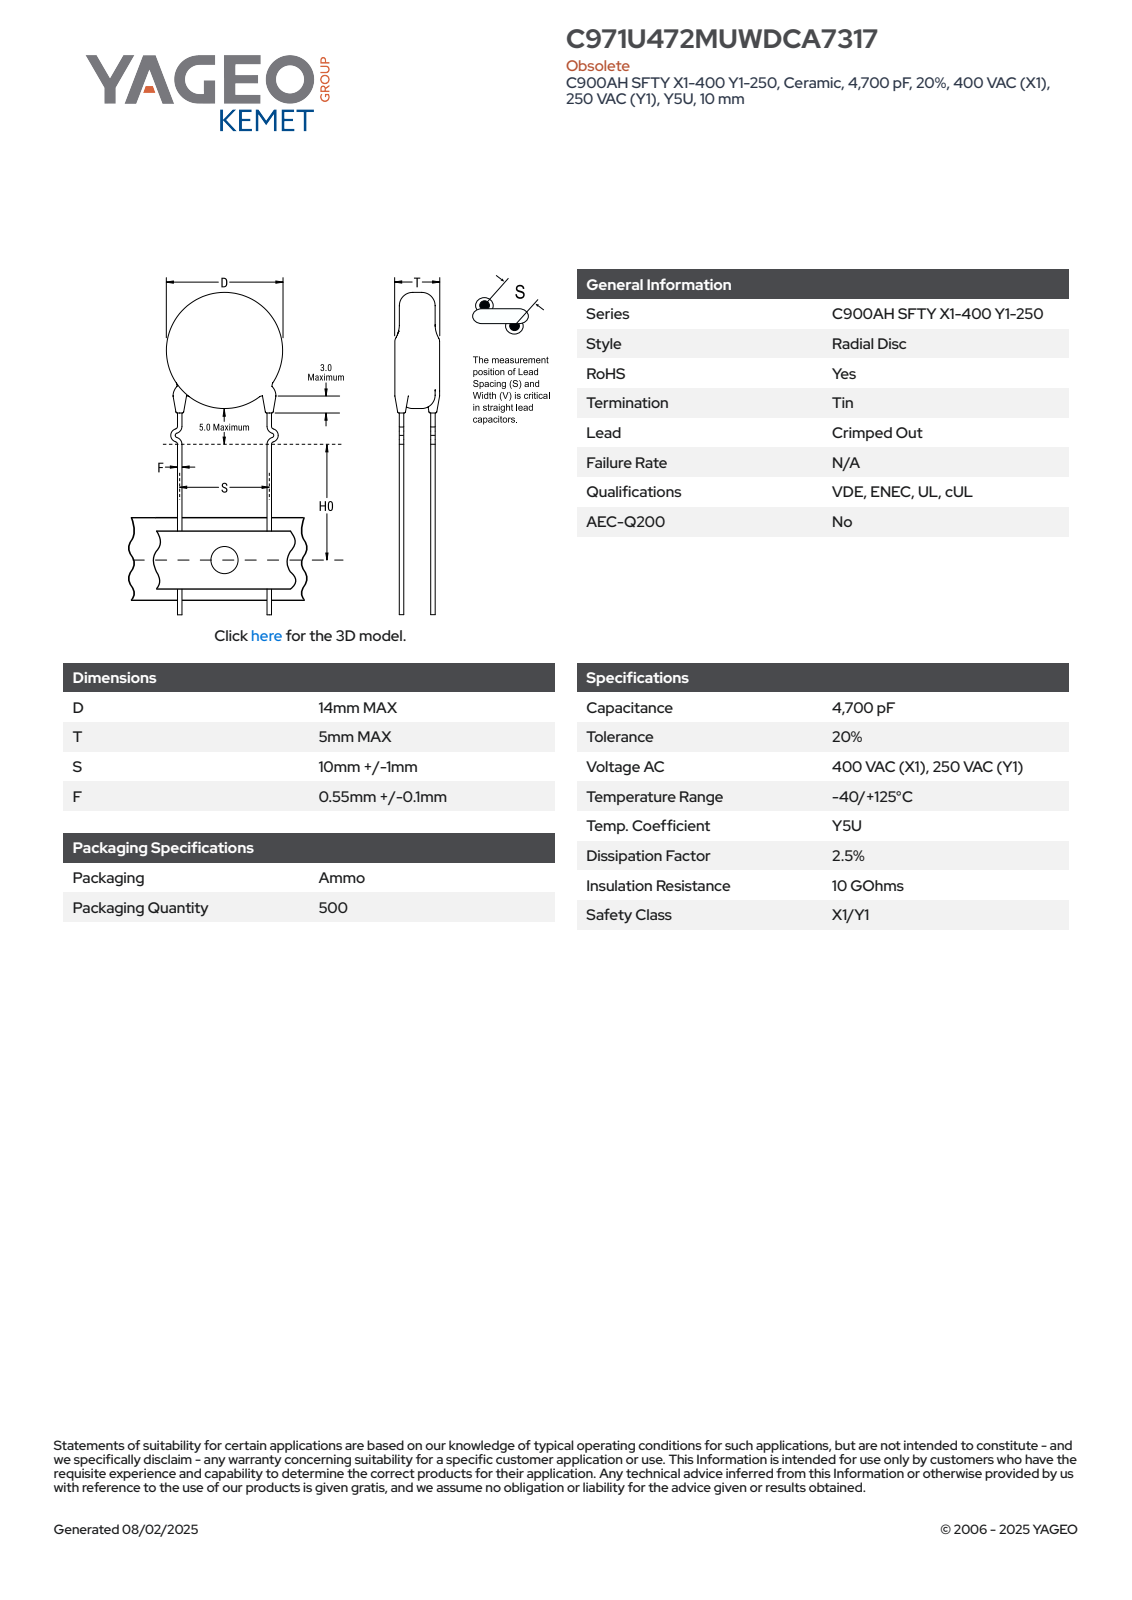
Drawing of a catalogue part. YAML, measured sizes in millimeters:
part_name: "CCD_KCOC900_D14T5S10LL20F0.55"
step_written_by: "SolidWorks 2014 (AUTOMOTIVE_DESIGN)"
units: millimeters
bodies: {solids: 4, faces: 85, planar: 63, cylindrical: 6, other: 16}
overall_size: [39, 15.15, 5]
volume: 774
surface_area: 629
round_bosses_or_shafts:
  - {diameter: 1.2, count: 2}
  - {diameter: 14, count: 1}
face_to_face_distances: [5, 7.74, 6.29, 1.45, 0.4, 5.94, 0.9, 1.17, 4.31, 4.48]
